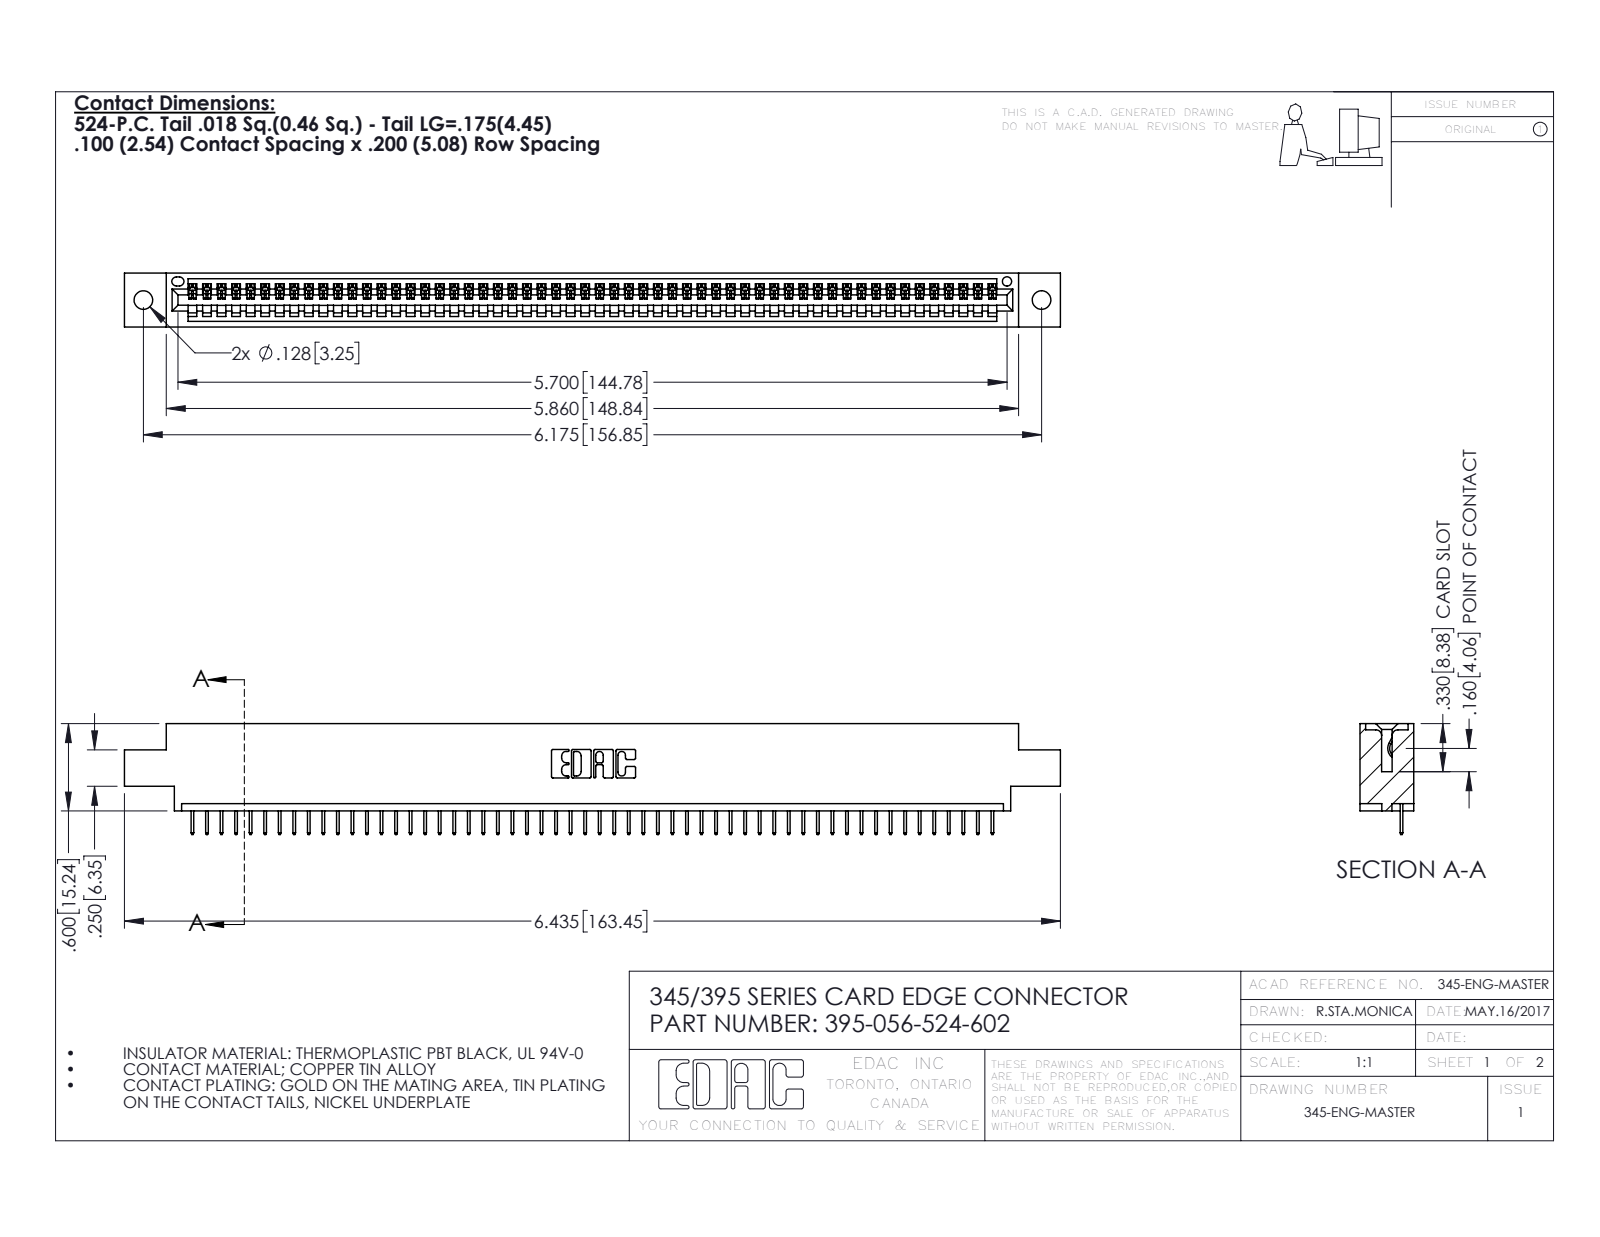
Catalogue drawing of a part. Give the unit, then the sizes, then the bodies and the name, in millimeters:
Units: millimetres
Overall size (bounding box): 163.4 × 19.4 × 9.4
Round holes (diameter × count): ⌀3.3 ×2, ⌀1.6 ×1
Partial cylindrical surfaces — rounded edges, fillets, slot ends (radius × count): R0.2 ×112, R0.3 ×22, R0.2 ×6, R0.8 ×6, R0.7 ×3, R0.8 ×2, R1 ×2, R0.4 ×1
Main face-to-face distances: 1.8, 7.6, 9.4, 5.1, 2.5, 6.9, 0.6, 5.7, 1.8, 4.4
Hole centre spacings: 6.9, 150.9, 156.8
Volume: 15 300 mm³ · Surface area: 19 630 mm²
Bodies: 57 solids, 3602 faces (2660 planar, 942 cylindrical, 0 other)
Part name (STEP PRODUCT): 395-056-524-602; 345 Part_0.170 Offset - 0.128 Dia; 345-292-001_345-293-124
STEP written by: SolidWorks 2016 (CONFIG_CONTROL_DESIGN)
